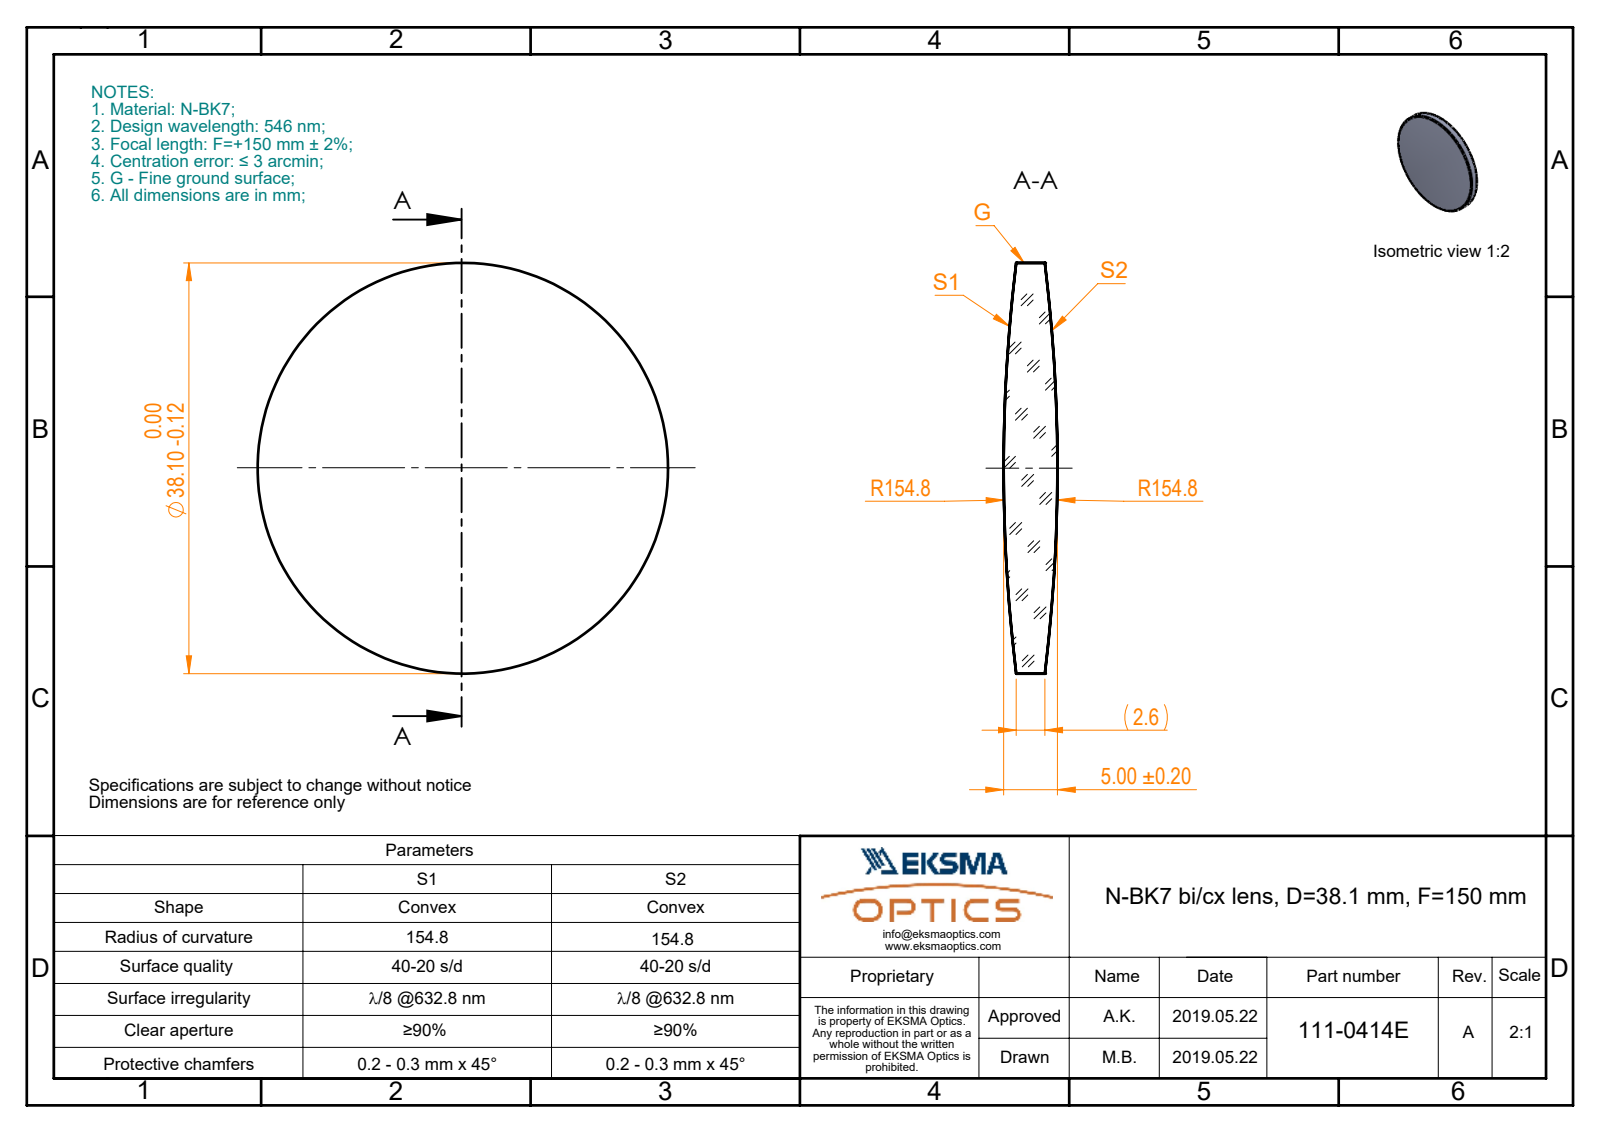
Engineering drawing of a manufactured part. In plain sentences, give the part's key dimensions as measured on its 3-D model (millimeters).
The part is named "111-0414E BK7 bi-cx 38.1 F150". Its 3-D file was written by "SolidWorks 2017 (CONFIG_CONTROL_DESIGN)". It is 1 solid with 6 faces: 0 planar, 2 cylindrical and 4 other. Overall it measures 38.1 by 38.1 by 5 millimeters. Its volume is 4 361 cubic millimeters and its surface area 2 606 square millimeters. Round bosses or shafts: 1 of diameter 38.1.
